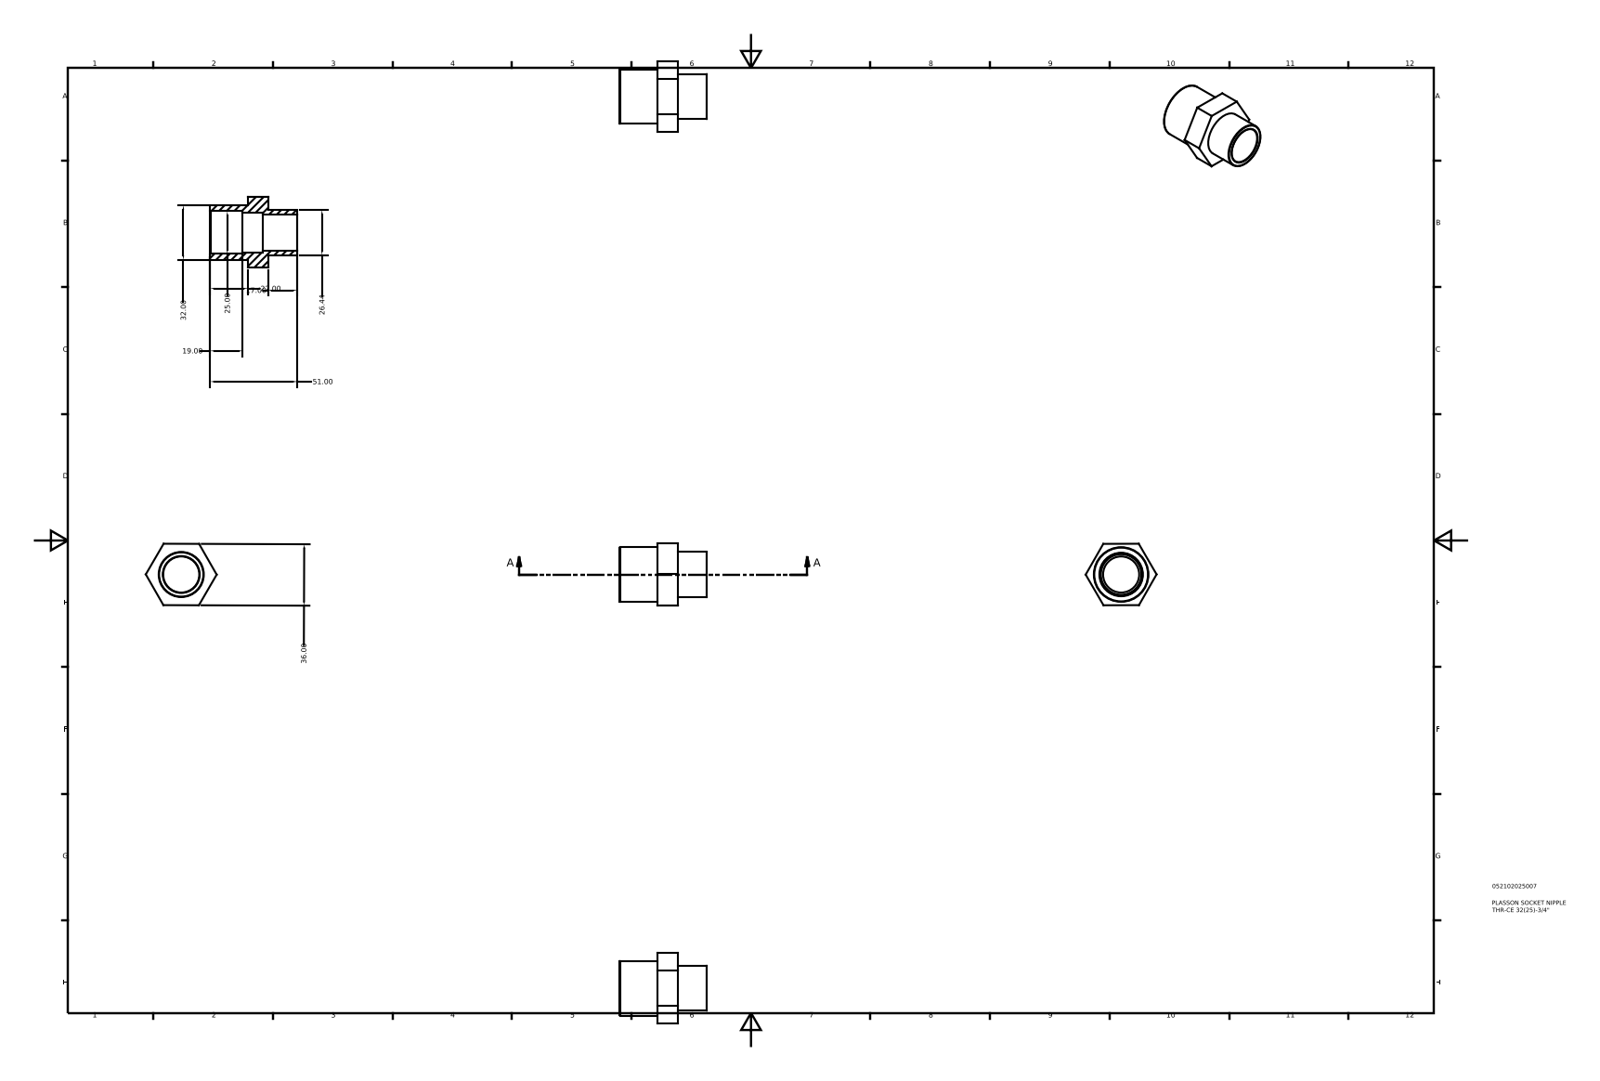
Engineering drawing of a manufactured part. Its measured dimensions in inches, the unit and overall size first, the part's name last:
Units: inches
Overall size (bounding box): 2.008 × 1.637 × 1.42
Round holes (diameter × count): ⌀0.833 ×1, ⌀0.935 ×1, ⌀0.984 ×1
Round bosses / shafts (diameter × count): ⌀1.26 ×1, ⌀1.041 ×1
Main face-to-face distances: 1.417, 0.472, 0.866, 1.339, 2.008, 1.142, 0.669, 1.205, 0.339, 0.134
Volume: 1.151 in³ · Surface area: 16.03 in²
Bodies: 1 solid, 21 faces (12 planar, 5 cylindrical, 4 other)
Part name (STEP PRODUCT): 052102025007
STEP written by: Autodesk Inventor 2015 (AUTOMOTIVE_DESIGN)
